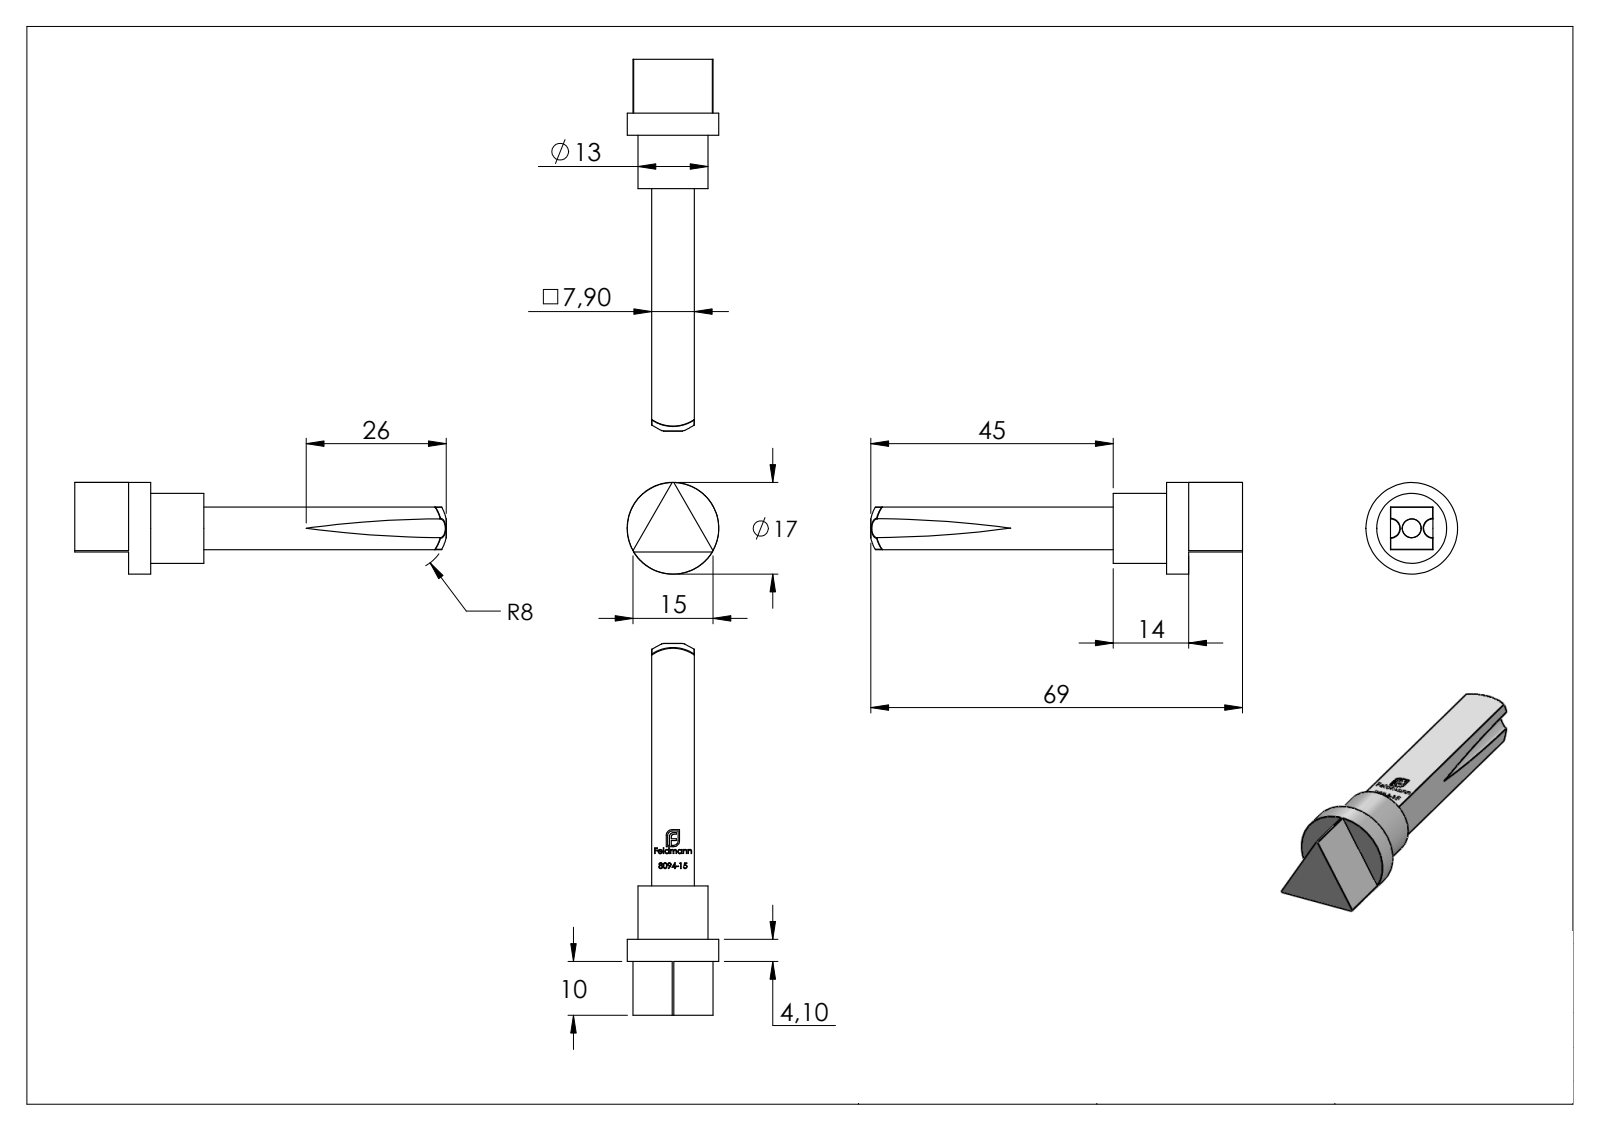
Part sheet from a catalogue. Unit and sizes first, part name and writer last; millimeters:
Units: millimetres
Overall size (bounding box): 69 × 17 × 17
Round bosses / shafts (diameter × count): ⌀17 ×1, ⌀13 ×1
Main face-to-face distances: 7.9, 0.42, 8.32, 10, 4.1, 14.1, 9.9, 14, 24, 45
Volume: 5 884 mm³ · Surface area: 2 981 mm²
Bodies: 1 solid, 276 faces (146 planar, 4 cylindrical, 126 other)
Part name (STEP PRODUCT): 8094-15
STEP written by: SolidWorks 2018 (CONFIG_CONTROL_DESIGN)
